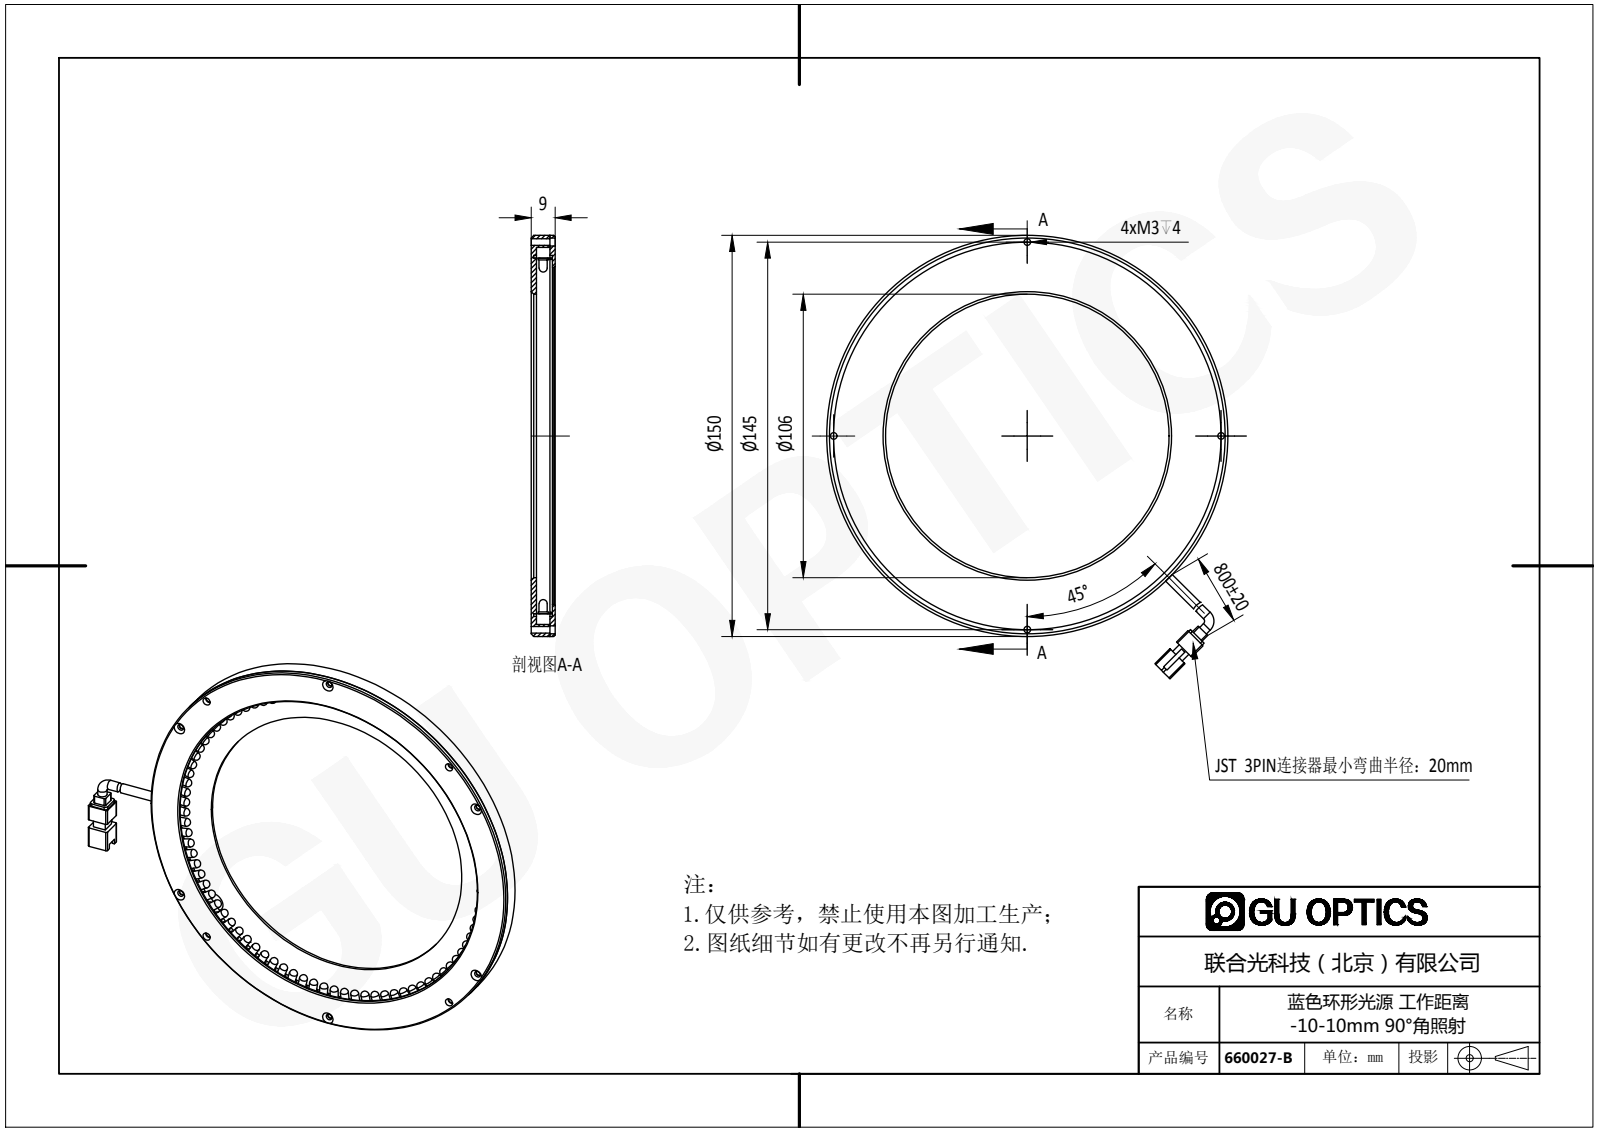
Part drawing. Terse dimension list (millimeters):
name: 660027-B
written by: SolidWorks 2016 (AUTOMOTIVE_DESIGN)
unit: mm
bodies: 95 solids, 1781 faces (1163 planar, 492 cylindrical, 126 other)
size: 177 × 150 × 11
volume: 41 228 mm³; area: 51 986 mm²
holes: 6× ⌀1.6, 6× ⌀2, 6× ⌀2.4, 4× ⌀2.5, 4× ⌀3, 2× ⌀8, 1× ⌀3.5, 1× ⌀106, 1× ⌀126, 1× ⌀132, 1× ⌀135, 1× ⌀141
bosses: 90× ⌀4, 90× ⌀3, 2× ⌀3.5, 1× ⌀150, 1× ⌀134, 1× ⌀133
rounds: 8× R0.5, 4× R1, 2× R2, 2× R3.5
face distances: 2, 7, 5, 1, 9, 8, 6, 0.5, 1.5, 3.77
hole spacings: 72.5, 72.49, 145, 88.27, 102.53, 115.03, 125.57, 133.96
